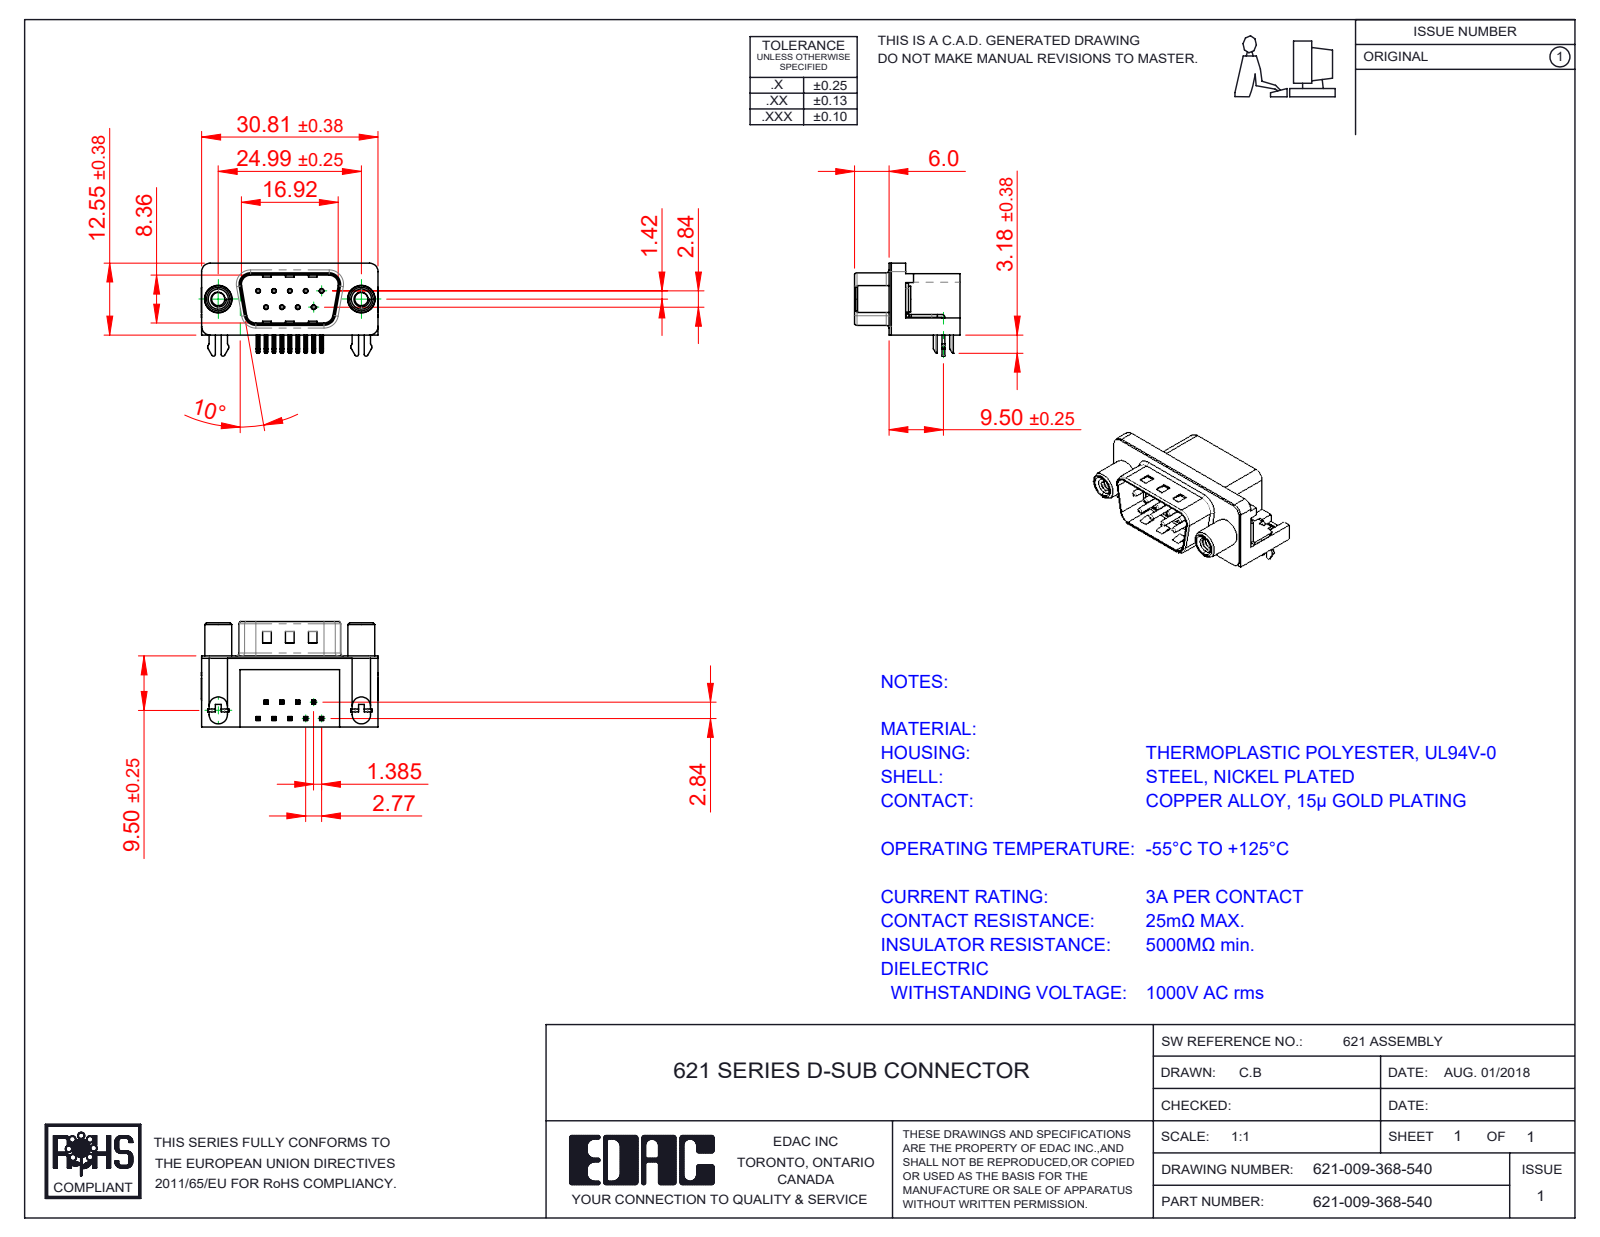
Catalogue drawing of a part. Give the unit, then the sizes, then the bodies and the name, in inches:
Units: inches
Overall size (bounding box): 1.216 × 0.724 × 0.64
Round holes (diameter × count): ⌀0.014 ×9, ⌀0.031 ×9, ⌀0.079 ×2, ⌀0.091 ×2, ⌀0.122 ×2, ⌀0.157 ×2, ⌀0.189 ×2, ⌀0.197 ×2
Round bosses / shafts (diameter × count): ⌀0.03 ×9, ⌀0.193 ×2, ⌀0.185 ×2, ⌀0.177 ×2, ⌀0.152 ×2, ⌀0.118 ×2
Partial cylindrical surfaces — rounded edges, fillets, slot ends (radius × count): R0.01 ×40, R0.005 ×18, R0.039 ×16, R0.02 ×9, R0.059 ×8, R0.063 ×8, R0.035 ×4, R0.079 ×4
Main face-to-face distances: 0.016, 0.472, 0.488, 0.407, 0.374, 0.098, 0.114, 0.083, 0.014, 0.421
Hole centre spacings: 0.124, 0.109, 0.218, 0.198, 0.198, 0.327, 0.294, 0.295
Volume: 0.204 in³ · Surface area: 7.277 in²
Bodies: 15 solids, 1105 faces (607 planar, 329 cylindrical, 169 other)
Part name (STEP PRODUCT): 621 4 Prong Board Lock; 621 Contact Bottom; 621 Round Threaded Standoff; 621 Contact Top (+3 more)
STEP written by: SolidWorks 2016 (CONFIG_CONTROL_DESIGN)
